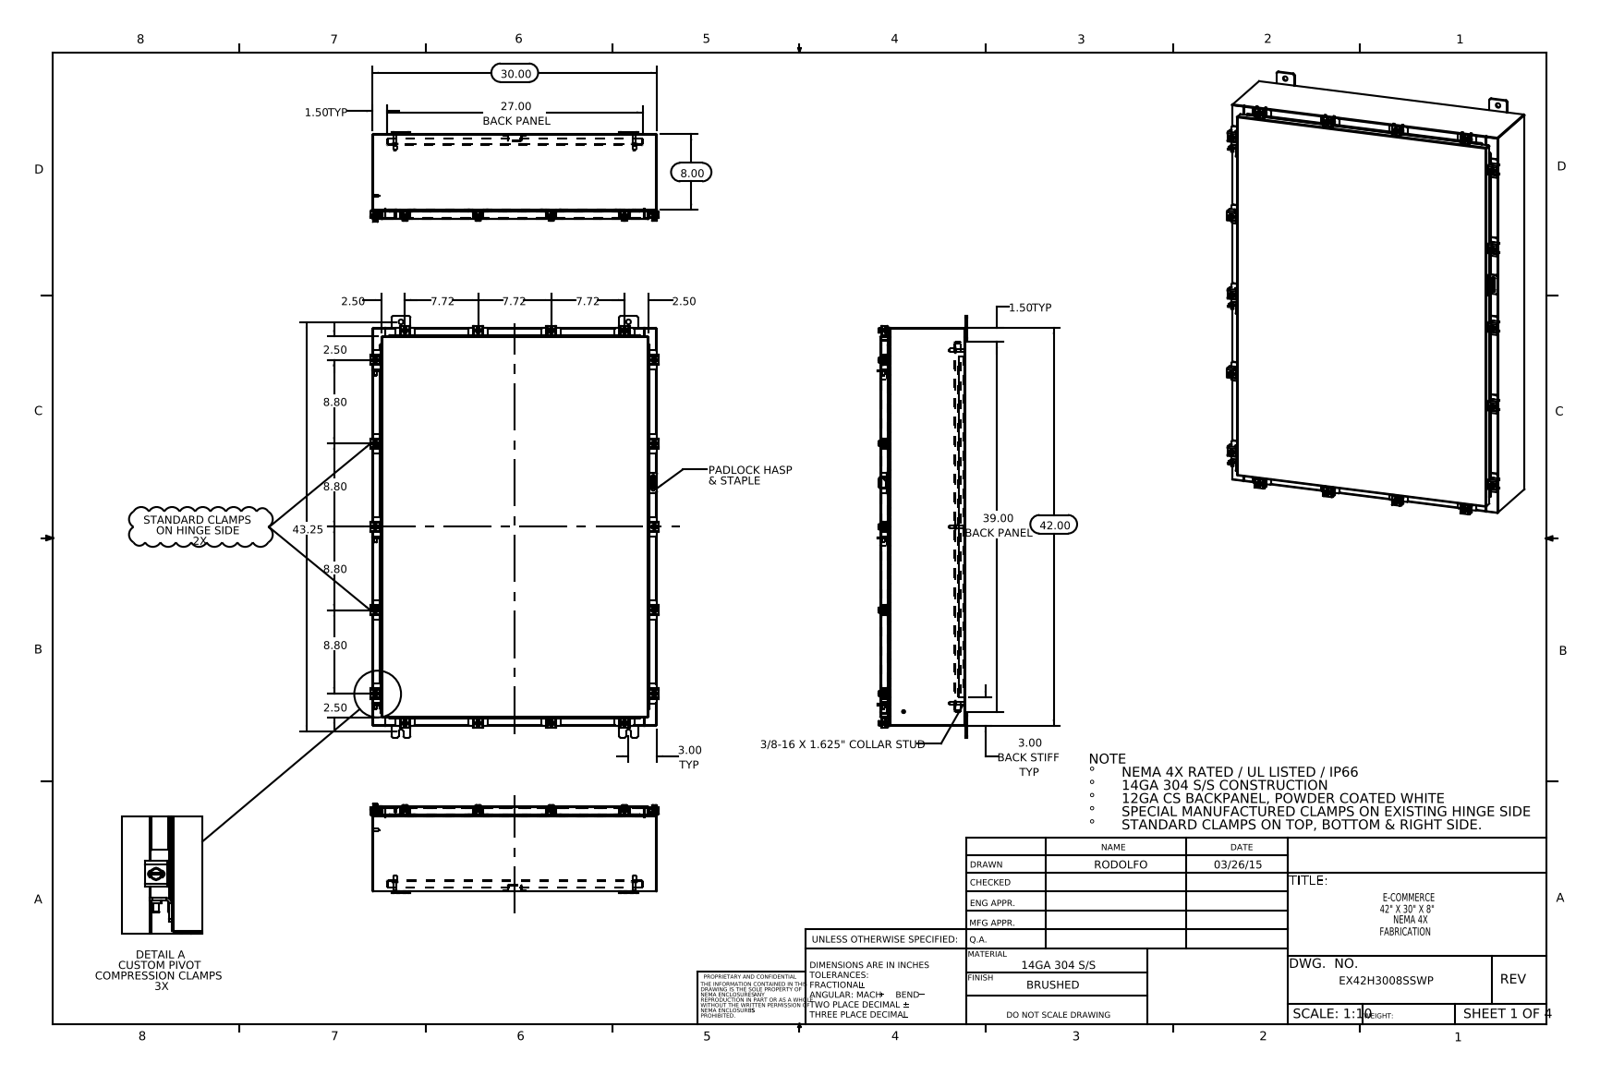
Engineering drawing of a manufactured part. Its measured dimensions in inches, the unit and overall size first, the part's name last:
Units: inches
Overall size (bounding box): 44.5 × 30.421 × 9.453
Round holes (diameter × count): ⌀0.213 ×18, ⌀0.26 ×18, ⌀0.5 ×10, ⌀0.125 ×1, ⌀0.25 ×1
Round bosses / shafts (diameter × count): ⌀0.5 ×18, ⌀0.25 ×18, ⌀0.399 ×15, ⌀0.625 ×6, ⌀0.375 ×6, ⌀0.33 ×6, ⌀0.315 ×2, ⌀0.236 ×2
Partial cylindrical surfaces — rounded edges, fillets, slot ends (radius × count): R0.06 ×76, R0.141 ×36, R0.12 ×33, R0.013 ×30, R0.09 ×27, R0.088 ×26, R0.05 ×25, R0.145 ×24
Main face-to-face distances: 0.075, 8.9, 8.826, 8.975, 0.104, 1, 1.075, 7.826, 7.9, 1.179
Hole centre spacings: 30.737, 29.451, 2.347, 4.44, 8.798, 17.719, 18.625, 20.752
Volume: 437.9 in³ · Surface area: 10 823 in²
Bodies: 116 solids, 2878 faces (1525 planar, 1123 cylindrical, 230 other)
Part name (STEP PRODUCT): EX42H3008SSWP Cover; EX42H3008SSWP Enclosure Stiffener; N-WMT04X30402202210-00 22104005_DEFAULT; EX42H3008SSWP (+8 more)
STEP written by: SolidWorks 2014 (CONFIG_CONTROL_DESIGN)
